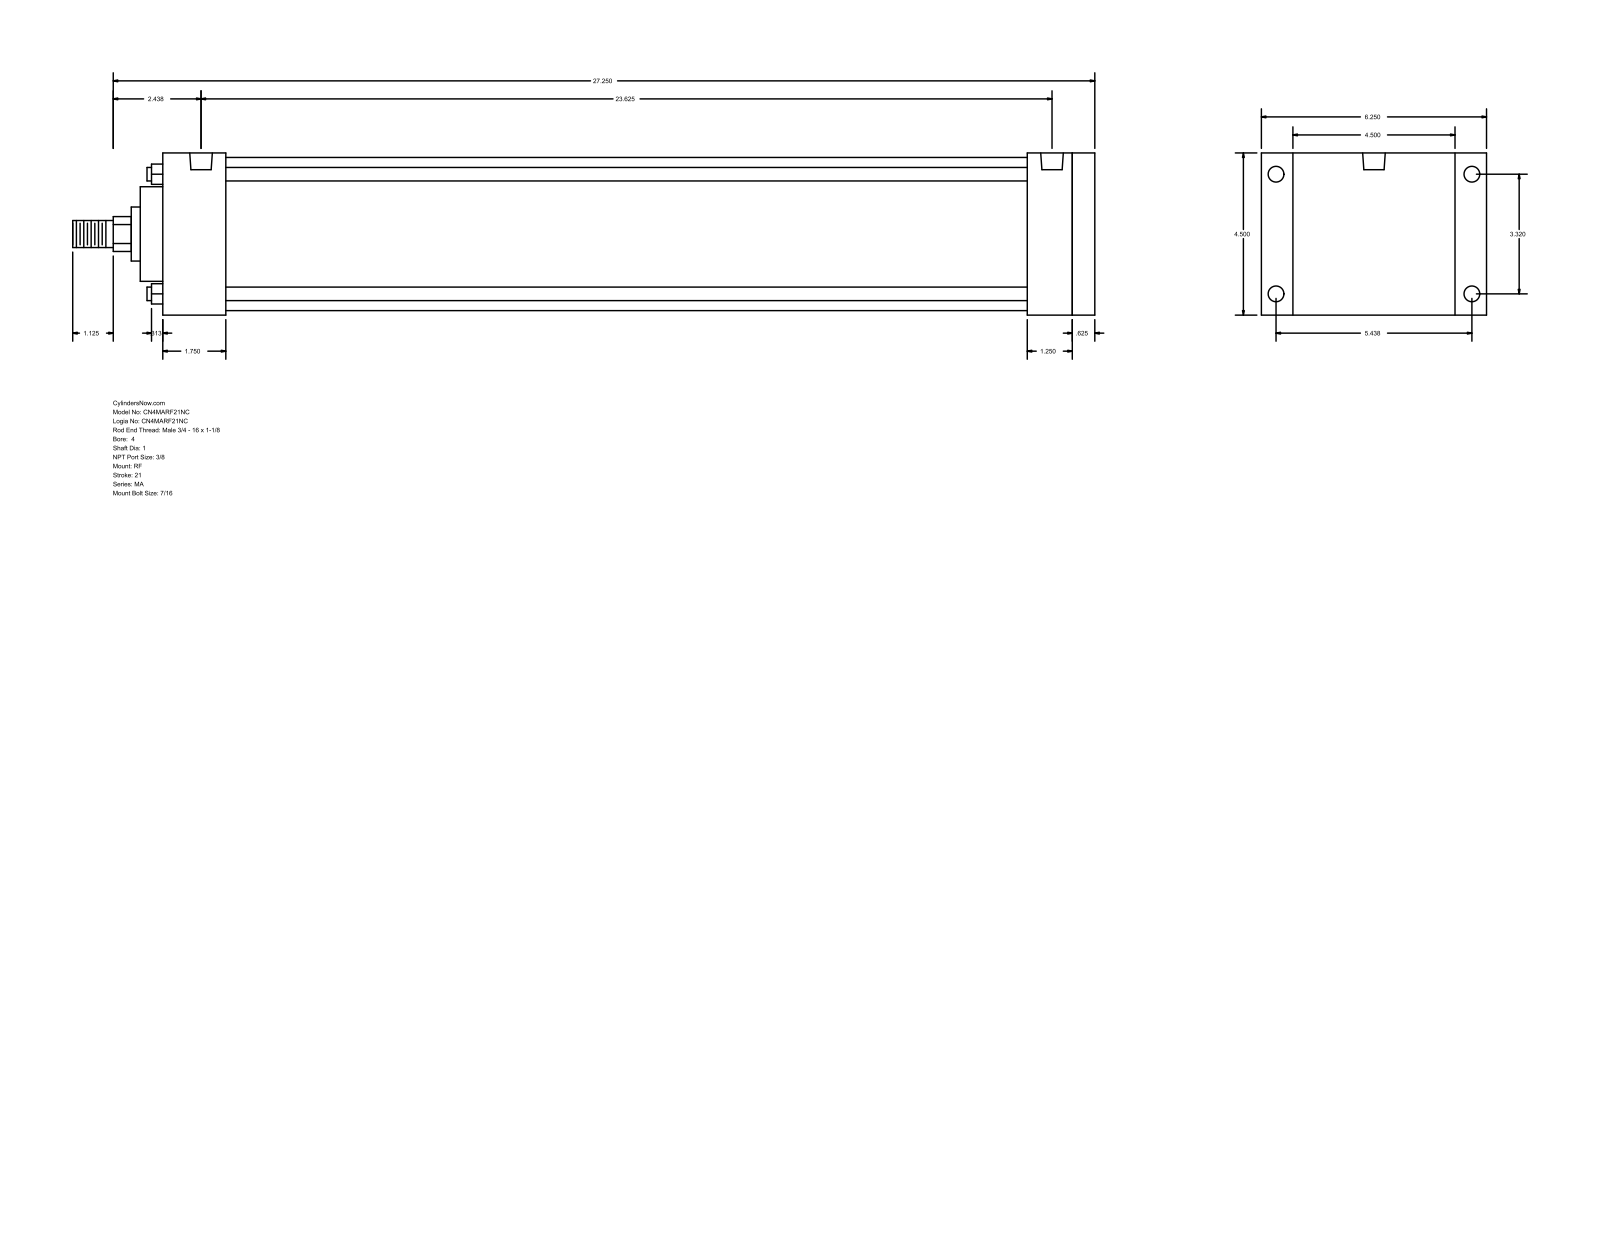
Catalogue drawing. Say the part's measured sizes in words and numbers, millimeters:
The part is named "MA_RF__0400_1". Its 3-D file was written by "GSSL Pune (CONFIG_CONTROL_DESIGN)". It is 0 solids with 94 faces: 65 planar, 29 cylindrical and 0 other. Overall it measures 720.73 by 158.75 by 114.3 millimeters. Round holes: 8 of diameter 11.11, 2 of diameter 15.93. Round bosses or shafts: 4 of diameter 9.53, 1 of diameter 107.95, 1 of diameter 66.67, 1 of diameter 38.1, 1 of diameter 25.4, 1 of diameter 19.05. Partial cylindrical surfaces (rounded edges, fillets, slot ends): 1 of radius 12.29. The main face-to-face distances are 114.3, 657.23, 641.35, 15.88, 22.23, 136.53, 609.6, 31.75, 47.63, 44.46. The hole center spacings are 4.76, 84.32, 138.12, 161.82, 590.56, 595.32, 600.08.
